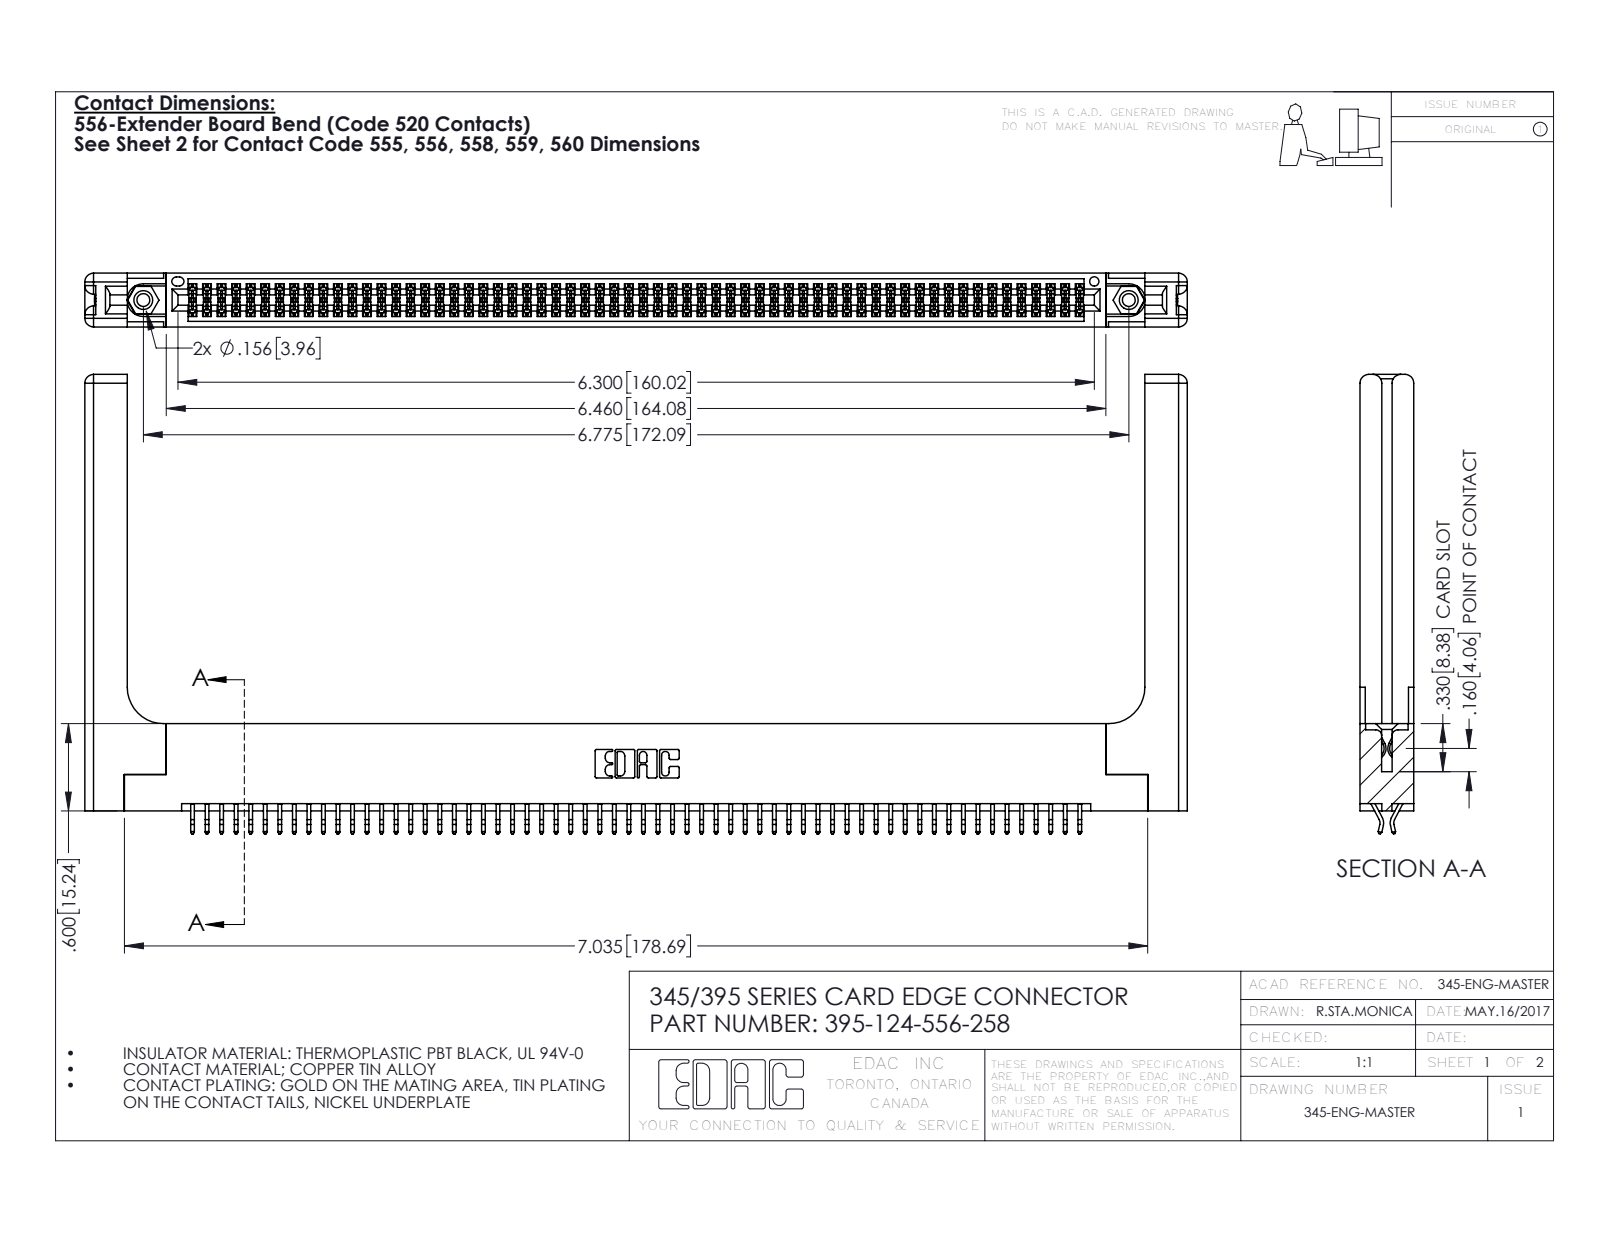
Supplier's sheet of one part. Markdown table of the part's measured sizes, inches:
| quantity | value |
| --- | --- |
| part name | 345 Part_Flush Mounting Lugs - 0.156 Dia-TH; 395-124-556-258; 345-220-058_345-220-058; 345-250-001_345-250-001-102 (+1 more) |
| STEP written by | SolidWorks 2016 (CONFIG_CONTROL_DESIGN) |
| units | inches |
| bodies | 129 solids, 7326 faces (4816 planar, 2450 cylindrical, 60 other) |
| overall size | 7.579 × 3.157 × 0.37 |
| volume | 1.669 in³ |
| surface area | 51.53 in² |
| round holes (diameter × count) | 0.089 × 2, 0.125 × 2, 0.156 × 2, 0.064 × 1 |
| round bosses / shafts (diameter × count) | 0.155 × 2 |
| partial cylindrical surfaces (radius × count) | 0.006 × 186, 0.01 × 22, 0.06 × 16, 0.007 × 6, 0.031 × 6, 0.026 × 3, 0.01 × 2, 0.014 × 2 |
| main face-to-face distances | 0.072, 0.298, 0.37, 0.2, 0.025, 0.098, 0.272, 0.225, 0.15, 0.148 |
| hole center spacings | 0.27, 6.539, 6.775 |
